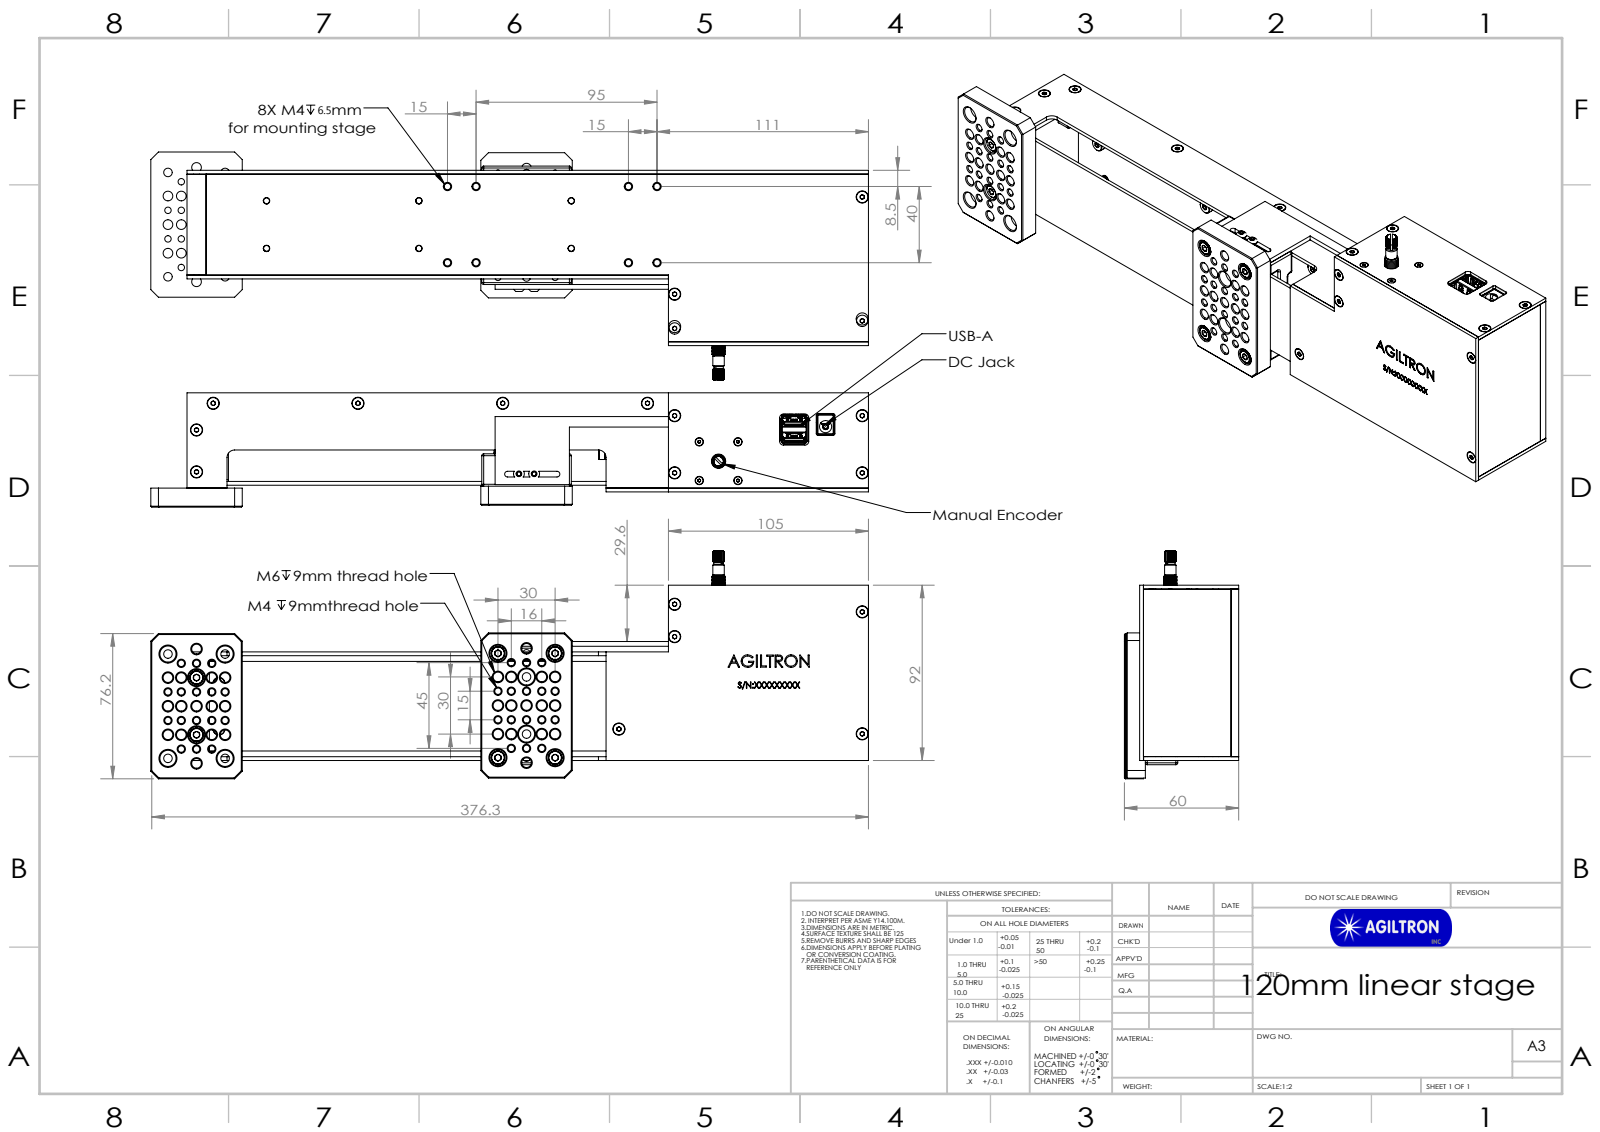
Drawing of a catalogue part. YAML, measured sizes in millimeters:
part_name: "NEO3535_REVERSE; 694106301002_PinContact.step_1; 1002354_SIDE PLATE G; QFN24_4MM (+8 more)"
step_written_by: "SolidWorks 2017 (CONFIG_CONTROL_DESIGN)"
units: millimeters
bodies: {solids: 136, faces: 7979, planar: 4365, cylindrical: 2494, other: 1120}
overall_size: [376.75, 119.6, 60]
volume: 507063
surface_area: 272305
round_holes:
  - {diameter: 3.4, count: 50}
  - {diameter: 5.1, count: 30}
  - {diameter: 2.55, count: 20}
  - {diameter: 3.5, count: 18}
  - {diameter: 4.5, count: 18}
  - {diameter: 8.5, count: 12}
  - {diameter: 1, count: 11}
  - {diameter: 0.48, count: 10}
  - {diameter: 0.48, count: 9}
  - {diameter: 2.5, count: 9}
  - {diameter: 2.46, count: 8}
  - {diameter: 3.3, count: 8}
round_bosses_or_shafts:
  - {diameter: 3, count: 29}
  - {diameter: 6, count: 25}
  - {diameter: 4, count: 24}
  - {diameter: 7, count: 11}
  - {diameter: 3.09, count: 10}
  - {diameter: 2.35, count: 9}
  - {diameter: 5.5, count: 8}
  - {diameter: 5.7, count: 5}
partial_cylinders:
  - {radius: 1, count: 57}
  - {radius: 0.25, count: 42}
  - {radius: 0.1, count: 39}
  - {radius: 0.3, count: 36}
  - {radius: 0.2, count: 28}
  - {radius: 0.5, count: 28}
  - {radius: 0.15, count: 26}
  - {radius: 0.6, count: 24}
face_to_face_distances: [2, 55, 3.5, 11, 50, 7, 39, 48, 10, 52]
hole_center_spacings: [80, 15, 30, 16.5, 16.77, 23.34, 30.92, 40]
